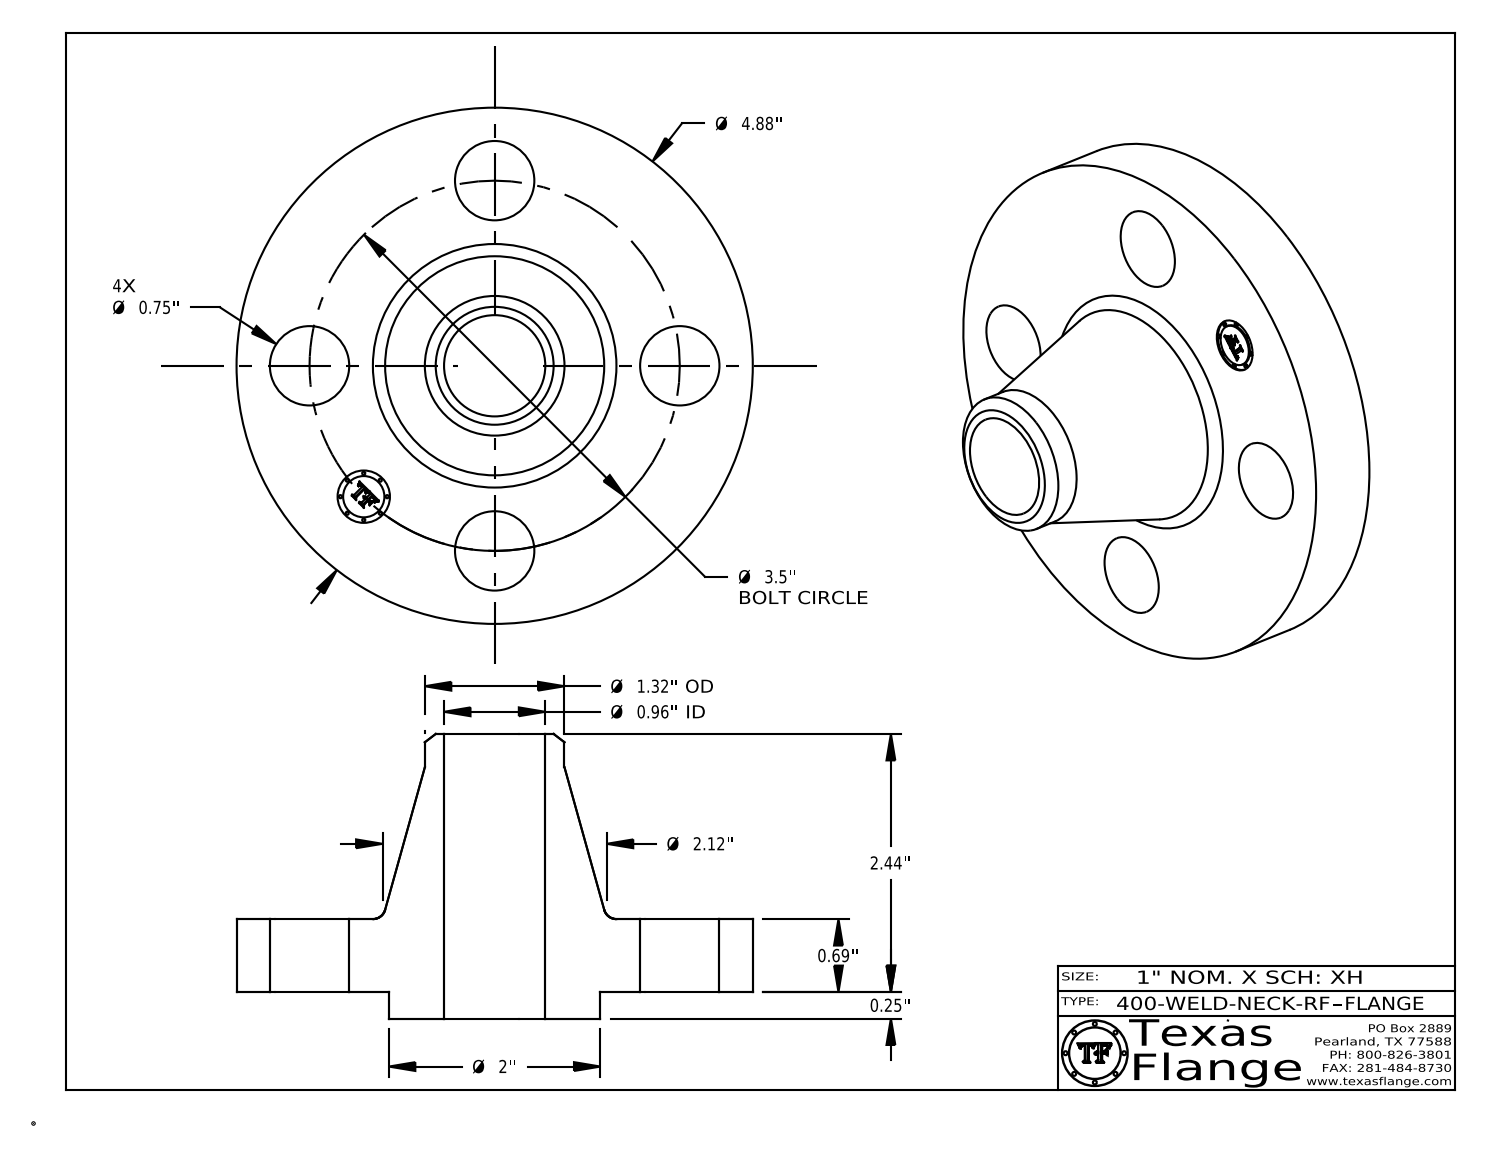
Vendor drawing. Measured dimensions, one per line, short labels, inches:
name: 400-WELD-NECK-RF
written by: CATIA V5 STEP AP214 (AUTOMOTIVE_DESIGN)
unit: in
bodies: 1 solid, 411 faces (369 planar, 36 cylindrical, 6 other)
size: 4.88 × 4.88 × 2.69
volume: 14.36 in³; area: 66.07 in²
holes: 4× ⌀0.75, 1× ⌀0.495, 1× ⌀0.957
bosses: 8× ⌀0.03, 1× ⌀4.88, 1× ⌀2, 1× ⌀1.32, 1× ⌀0.39
face distances: 0.69, 0.25, 0.94, 2.69, 2.44, 1.75, 0.015, 0.925, 0.675, 1.765
hole spacings: 1.75, 2.475, 1.339, 3.233, 3.5
